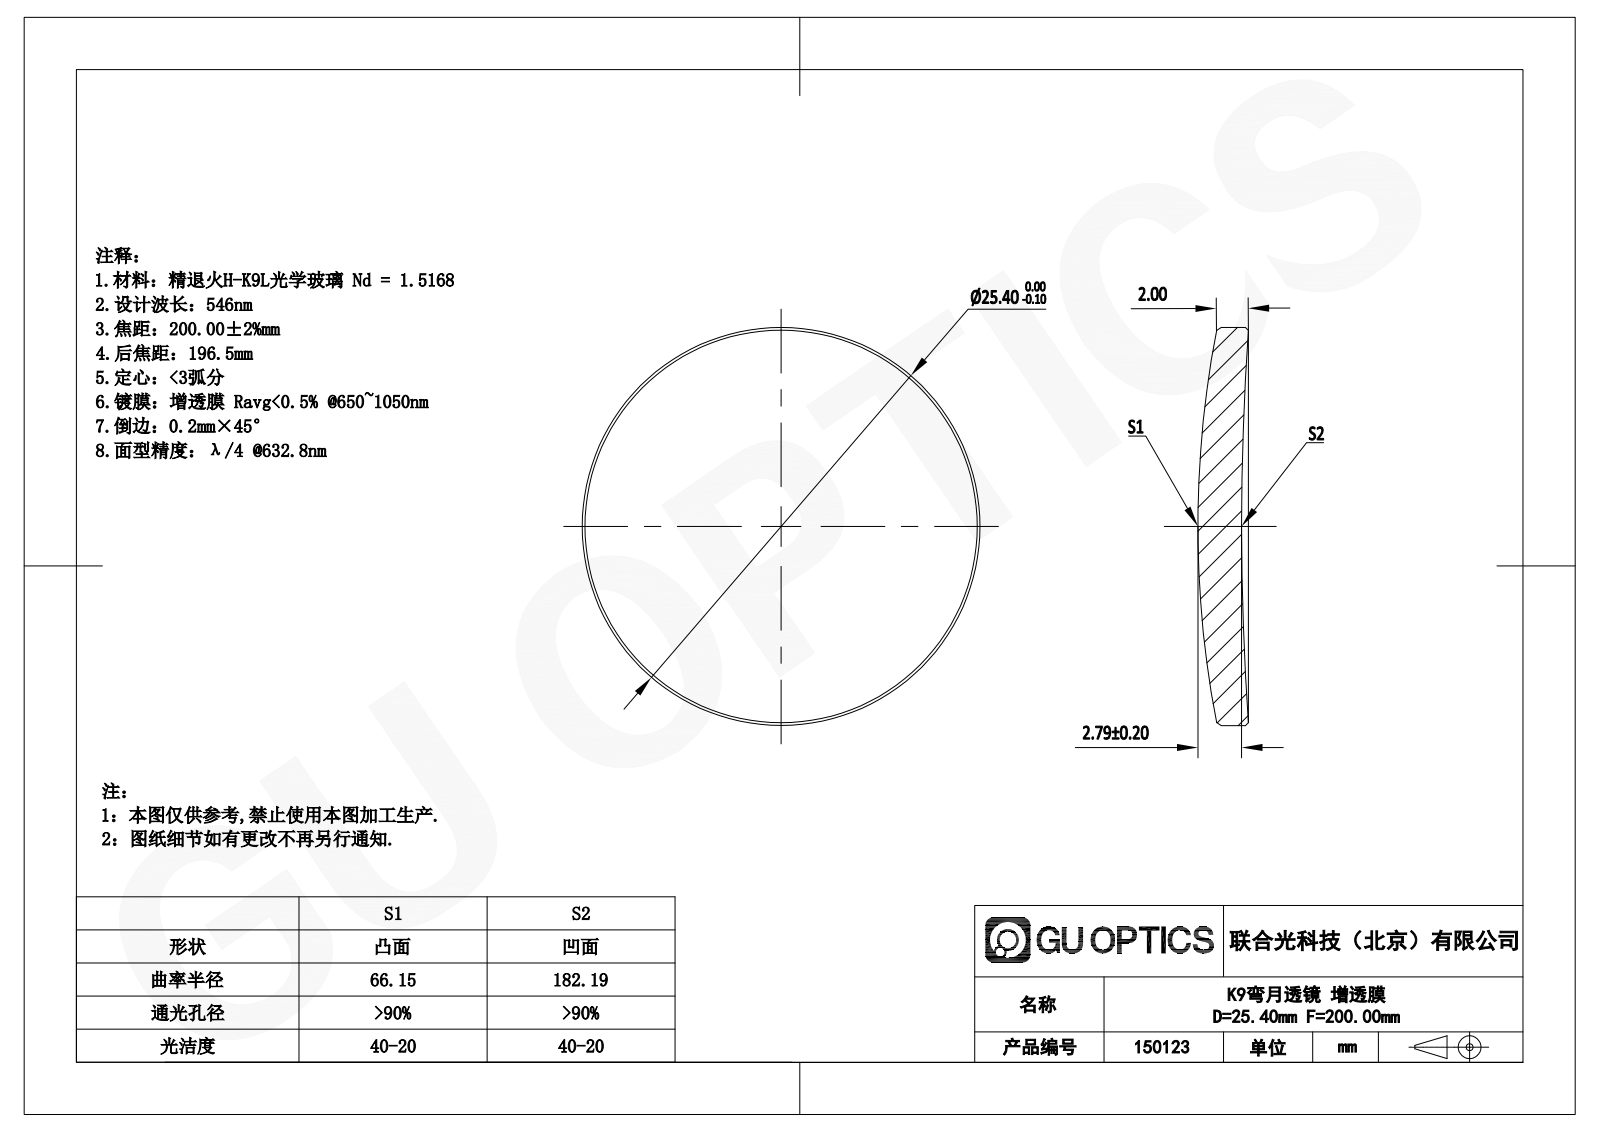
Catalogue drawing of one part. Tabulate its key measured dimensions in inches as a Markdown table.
| quantity | value |
| --- | --- |
| part name | GLM1-025B-200-NIR |
| STEP written by | SolidWorks 2022 (AUTOMOTIVE_DESIGN) |
| units | inches |
| bodies | 1 solid, 10 faces (0 planar, 2 cylindrical, 8 other) |
| overall size | 1 × 1 × 0.127 |
| volume | 0.074 in³ |
| surface area | 1.798 in² |
| round bosses / shafts (diameter × count) | 1 × 1 |
